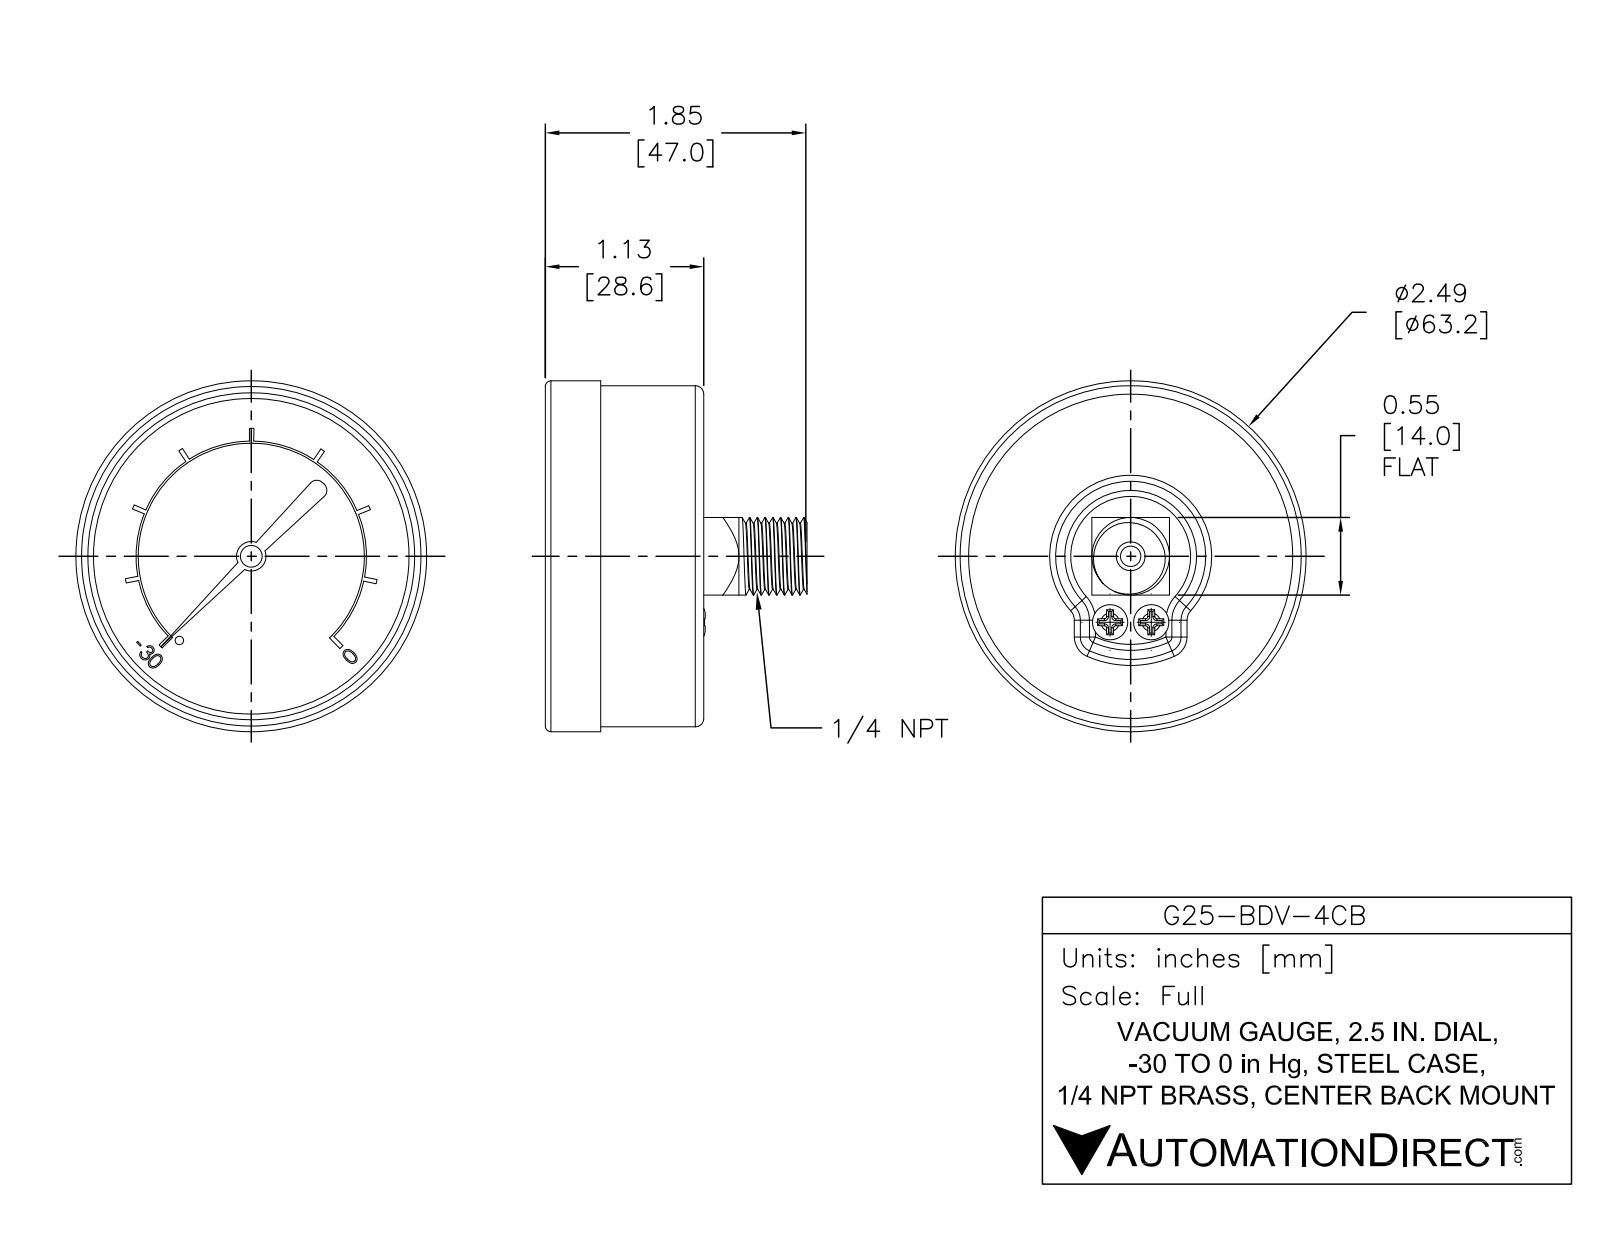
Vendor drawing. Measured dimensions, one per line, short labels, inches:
name: G25-BDV-4CB
written by: SolidWorks 2021 (AUTOMOTIVE_DESIGN)
unit: in
bodies: 1 solid, 204 faces (103 planar, 32 cylindrical, 69 other)
size: 2.49 × 2.49 × 1.858
volume: 4.301 in³; area: 22.47 in²
holes: 1× ⌀0.145, 1× ⌀2.185
bosses: 2× ⌀0.25, 1× ⌀2.49, 1× ⌀2.421, 1× ⌀0.55, 1× ⌀0.178, 1× ⌀0.099, 1× ⌀0.04
rounds: 4× R0.06, 2× R0.03, 1× R0.115, 1× R0.813, 1× R0.823
face distances: 0.835, 0.1, 1.125, 0.29, 0.735, 1.025, 0.731, 0.631, 0.104, 0.394
